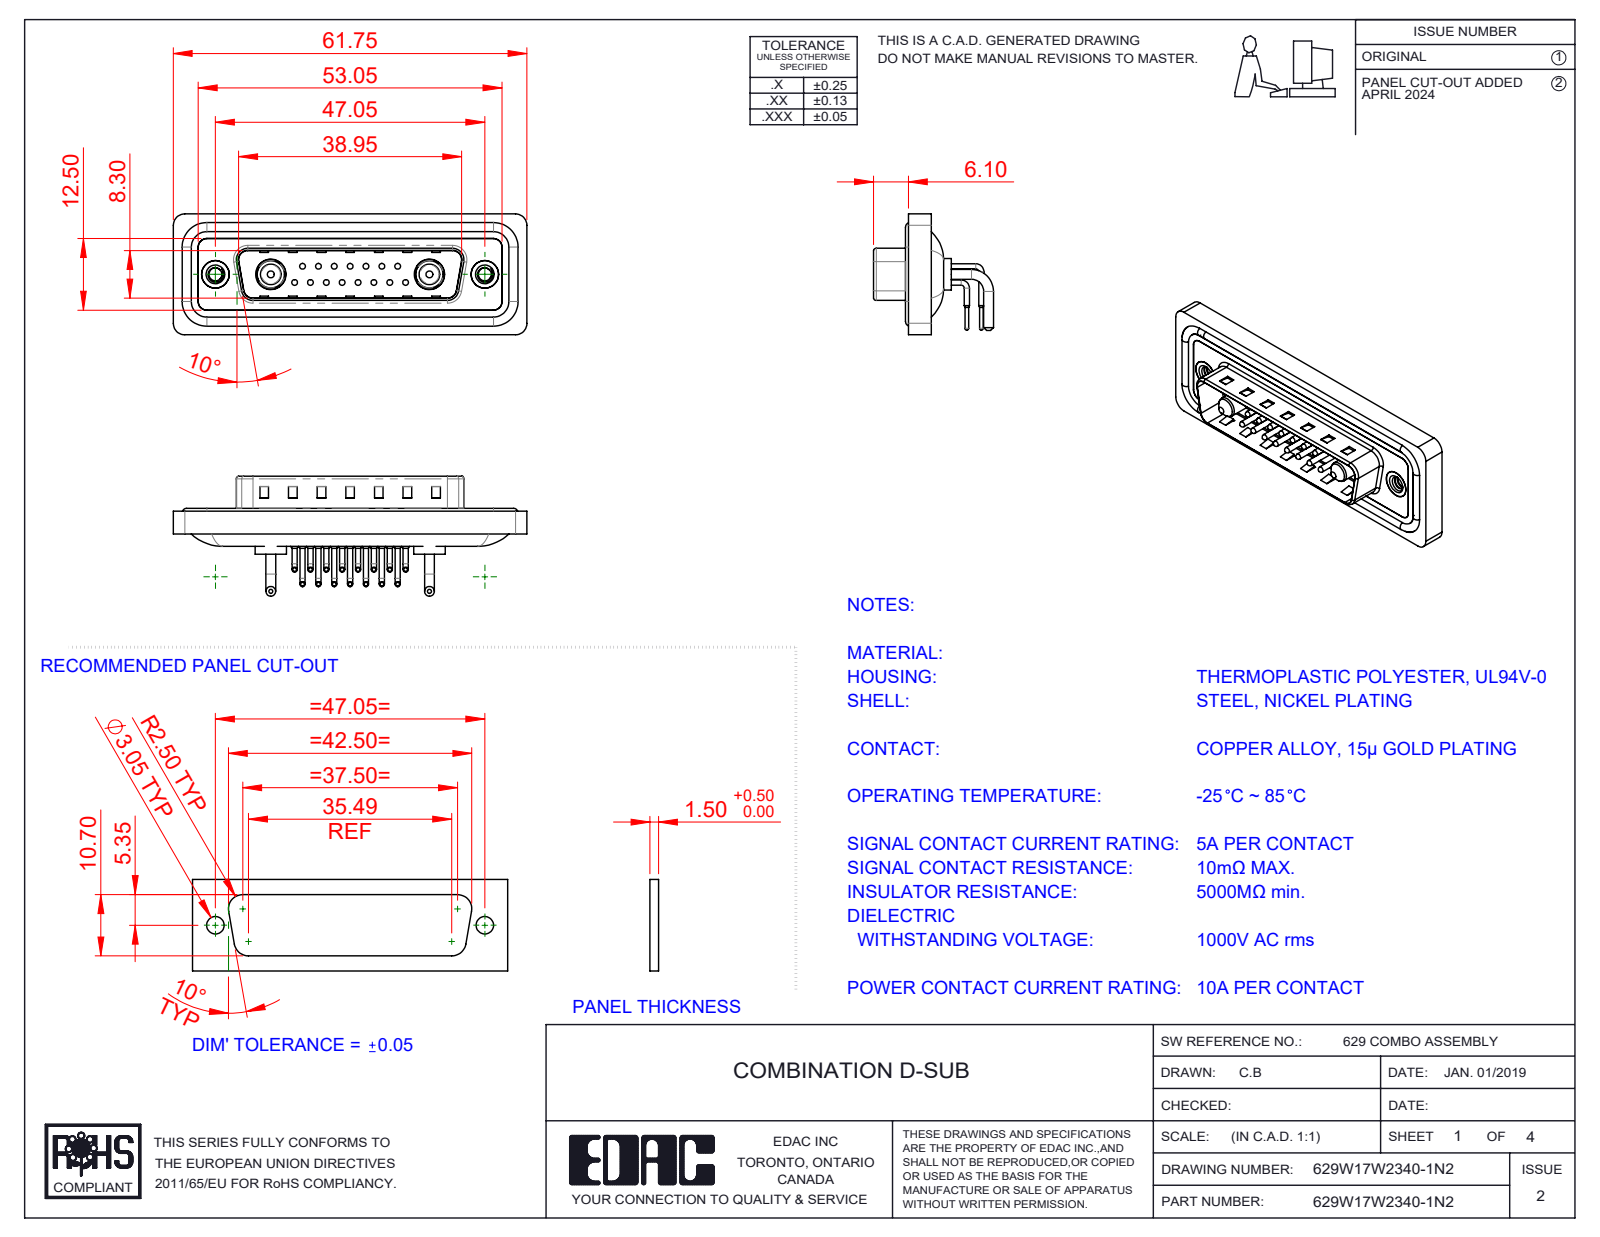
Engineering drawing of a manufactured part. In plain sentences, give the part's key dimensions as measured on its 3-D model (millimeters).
The part is named "629Combo Threaded Rivet_2; 629Combo Shell Front_25 Contacts; 629Combo Shell Rear_25 Contacts; 629Combo Housing_17W2 (+5 more)". Its 3-D file was written by "SolidWorks 2023 (CONFIG_CONTROL_DESIGN)". It is 26 solids with 2219 faces: 1189 planar, 770 cylindrical and 260 other. Overall it measures 61.75 by 21.1 by 20.95 millimeters. Its volume is 7 407 cubic millimeters and its surface area 12 500 square millimeters. Round holes: 15 of diameter 0.75, 15 of diameter 1.6, 15 of diameter 2, 2 of diameter 2.26, 2 of diameter 4, 2 of diameter 4.8, 2 of diameter 4.85, 2 of diameter 5, 2 of diameter 5.3. Round bosses or shafts: 30 of diameter 0.9, 15 of diameter 1.5, 15 of diameter 1, 15 of diameter 0.65, 4 of diameter 1.7, 4 of diameter 1.6, 2 of diameter 5.5, 2 of diameter 5.2. Partial cylindrical surfaces (rounded edges, fillets, slot ends): 18 of radius 1.5, 18 of radius 2, 15 of radius 1.01, 8 of radius 0.5, 8 of radius 1.6, 4 of radius 0.25, 4 of radius 0.6, 4 of radius 0.65. The main face-to-face distances are 0.4, 2.9, 0.8, 4.1, 1.1, 2.1, 1.6, 4.5, 1.5, 2.5. The hole center spacings are 3.16, 2.77, 5.54, 8.31, 5.04, 7.49, 11.08, 5.03.
